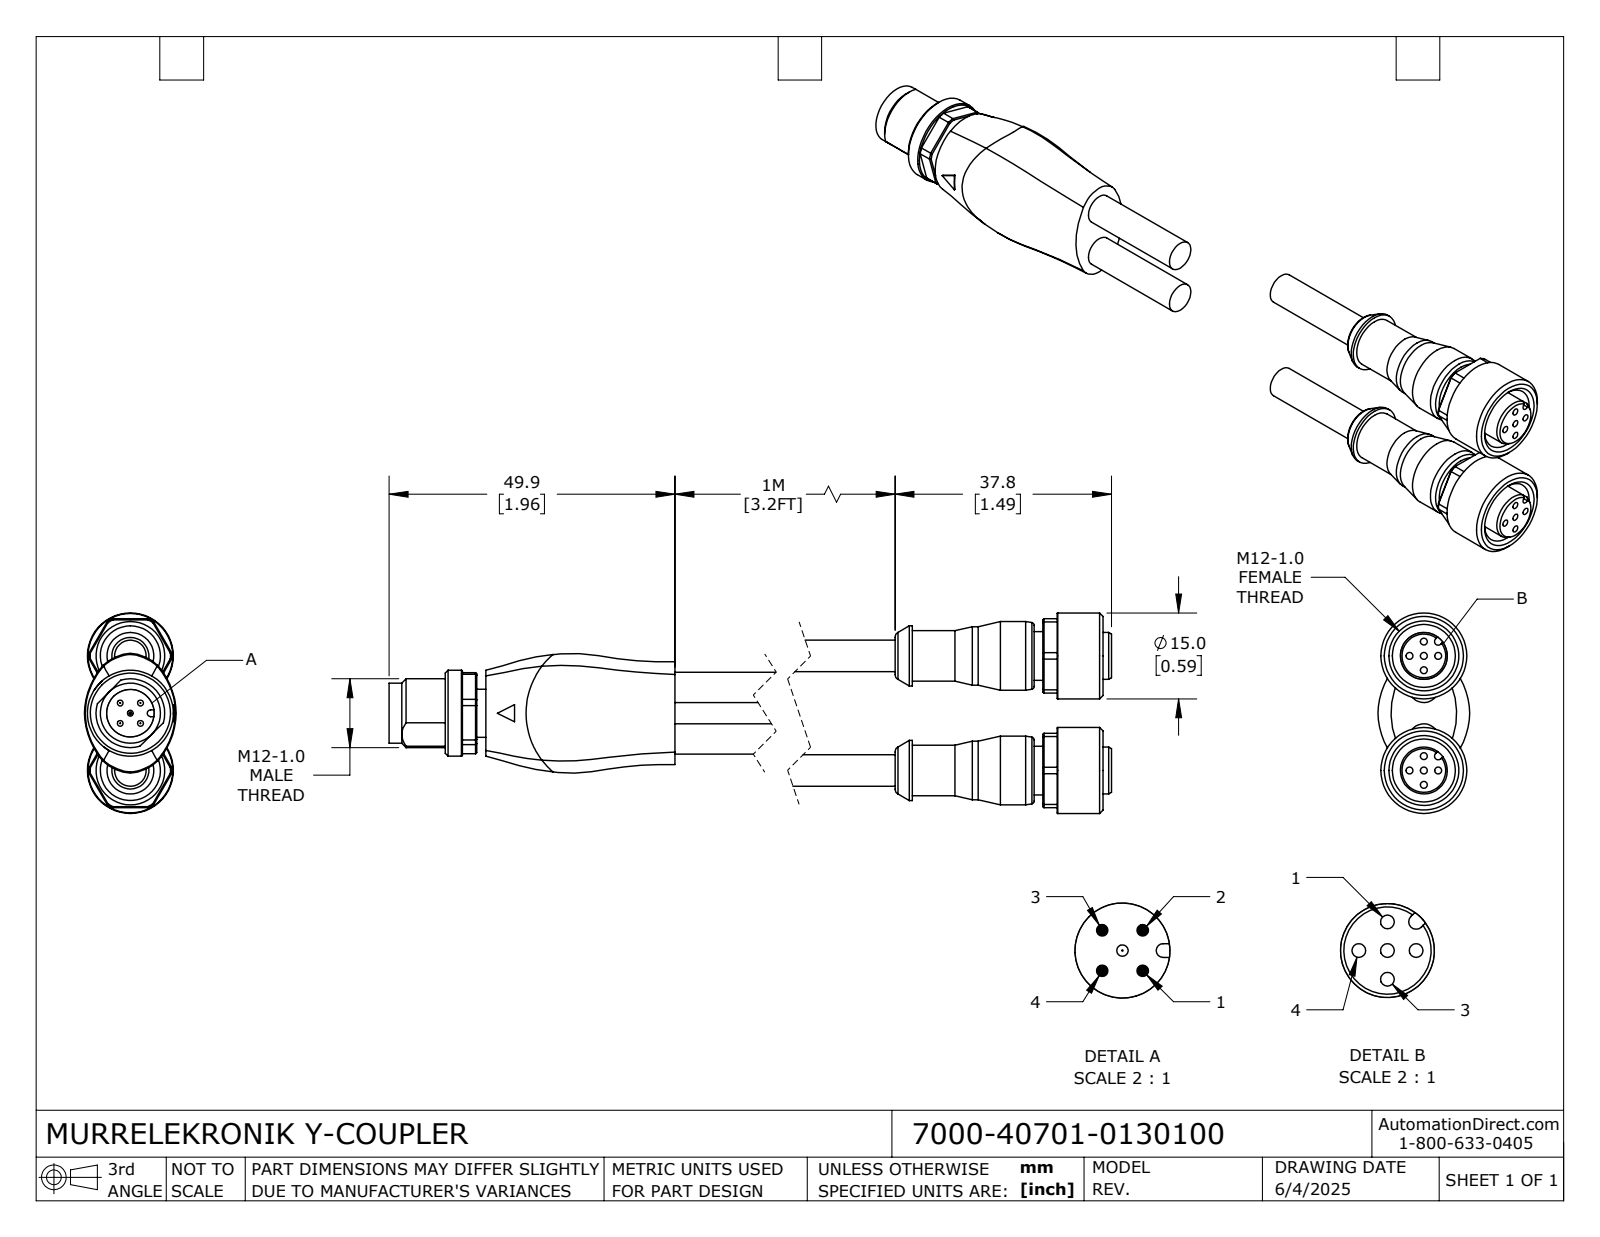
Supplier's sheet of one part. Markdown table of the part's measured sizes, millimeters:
| quantity | value |
| --- | --- |
| part name | 7000-40701-0130100; 7000-40701-0130030_FEMALE; 7000-40701-0130030_MALE |
| STEP written by | SolidWorks 2024 (CONFIG_CONTROL_DESIGN) |
| units | millimeters |
| bodies | 3 solids, 283 faces (93 planar, 103 cylindrical, 87 other) |
| overall size | 152.7 × 35 × 16.01 |
| volume | 17 544 mm³ |
| surface area | 9 297 mm² |
| round holes (diameter × count) | 1.2 × 10, 11 × 2, 8.3 × 1 |
| round bosses / shafts (diameter × count) | 1 × 5, 15 × 3, 10.5 × 3, 12 × 2, 10.2 × 2, 8.8 × 2, 8.5 × 2, 8.2 × 2 |
| partial cylindrical surfaces (radius × count) | 7.2 × 3, 0.65 × 2, 0.6 × 1, 6 × 1 |
| main face-to-face distances | 3, 12, 33, 1.5, 13, 123.8, 90.8, 134.3, 10.5, 8 |
| hole center spacings | 2.5, 3.54, 20, 5, 10.31, 17.68, 20.16, 22.64 |
